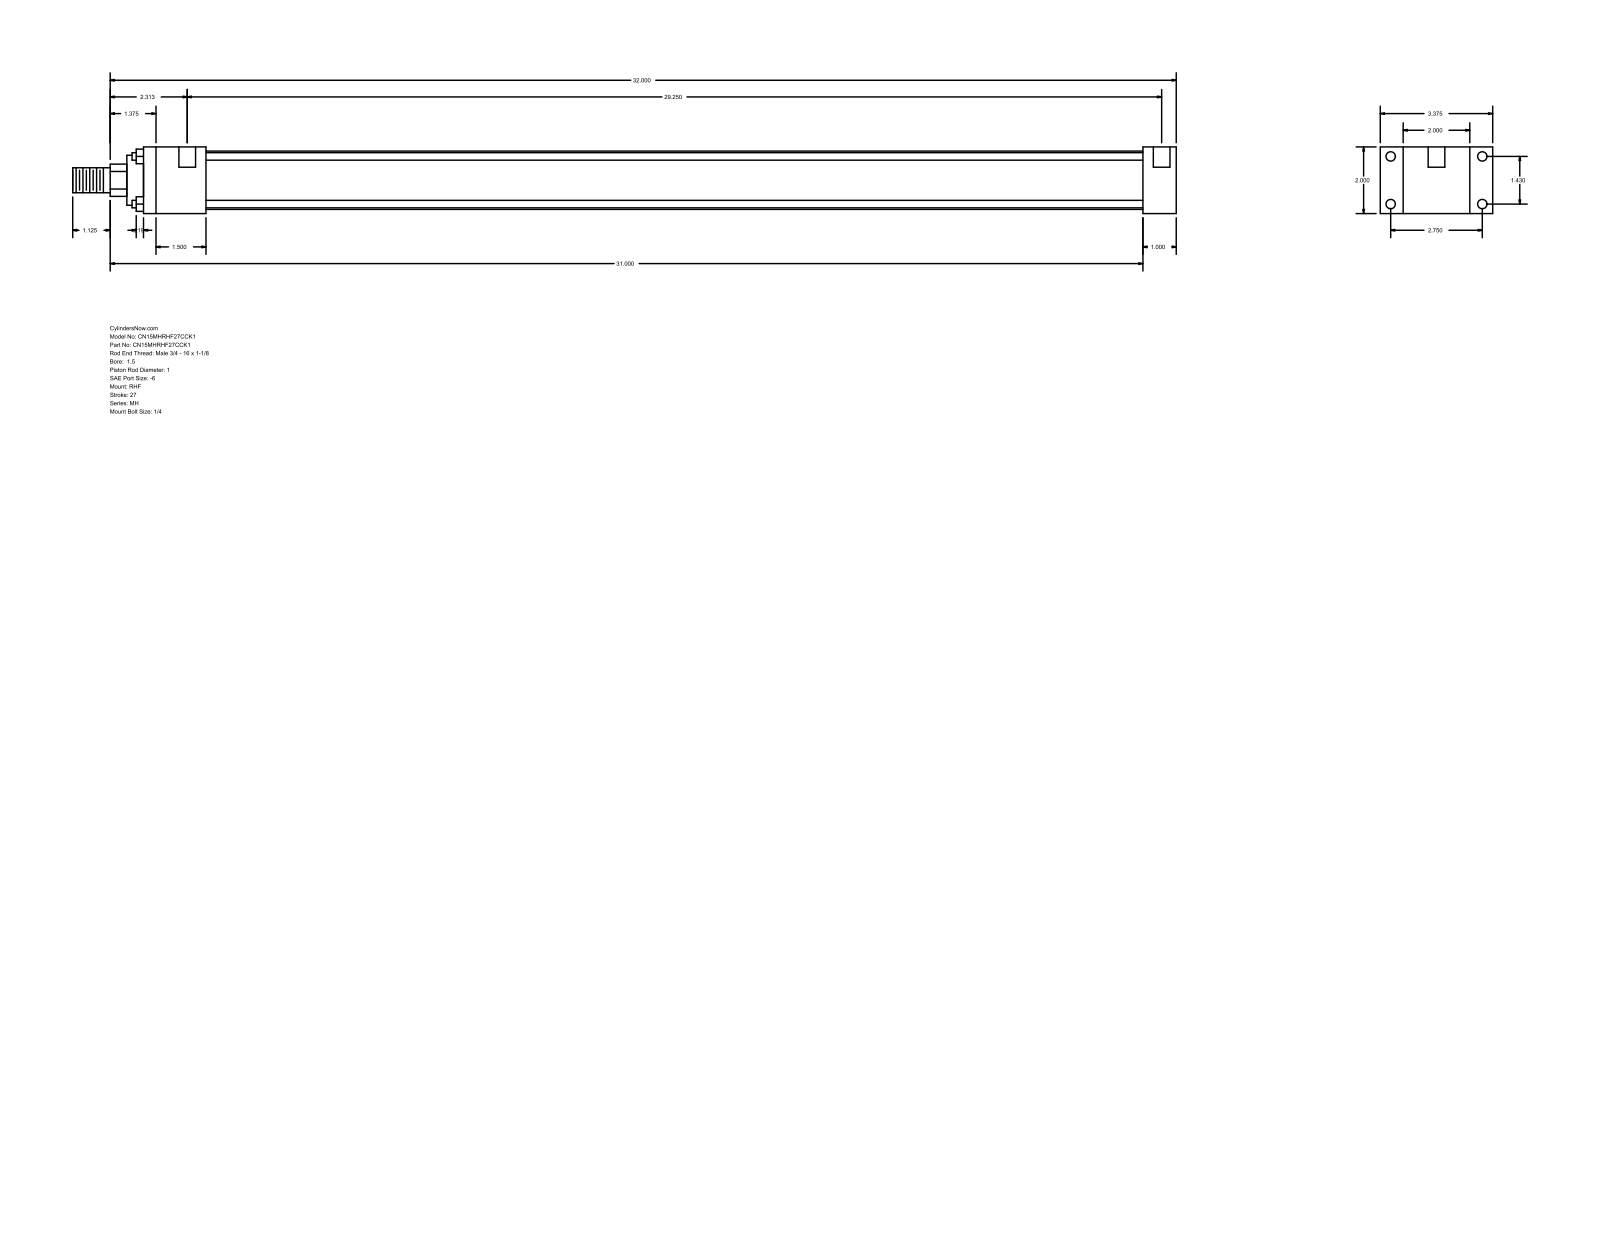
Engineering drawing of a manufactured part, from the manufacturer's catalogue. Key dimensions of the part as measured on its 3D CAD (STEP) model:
Part name (STEP PRODUCT): MH_RHF__0150_1
STEP written by: GSSL Pune (CONFIG_CONTROL_DESIGN)
Units: millimetres
Bodies: 0 solids, 88 faces (60 planar, 28 cylindrical, 0 other)
Overall size (bounding box): 841.38 × 85.72 × 50.8
Round holes (diameter × count): ⌀5.56 ×4, ⌀7.14 ×4, ⌀12.7 ×2
Round bosses / shafts (diameter × count): ⌀5.71 ×4, ⌀44.45 ×1, ⌀38.1 ×1, ⌀25.4 ×1, ⌀19.05 ×1
Partial cylindrical surfaces — rounded edges, fillets, slot ends (radius × count): R12.29 ×1
Main face-to-face distances: 50.8, 25.4, 17.46, 68.26, 85.72, 787.4, 762, 47.63, 714.37, 739.77
Hole centre spacings: 36.32, 69.84, 78.72, 746.13, 3.18, 742.95
